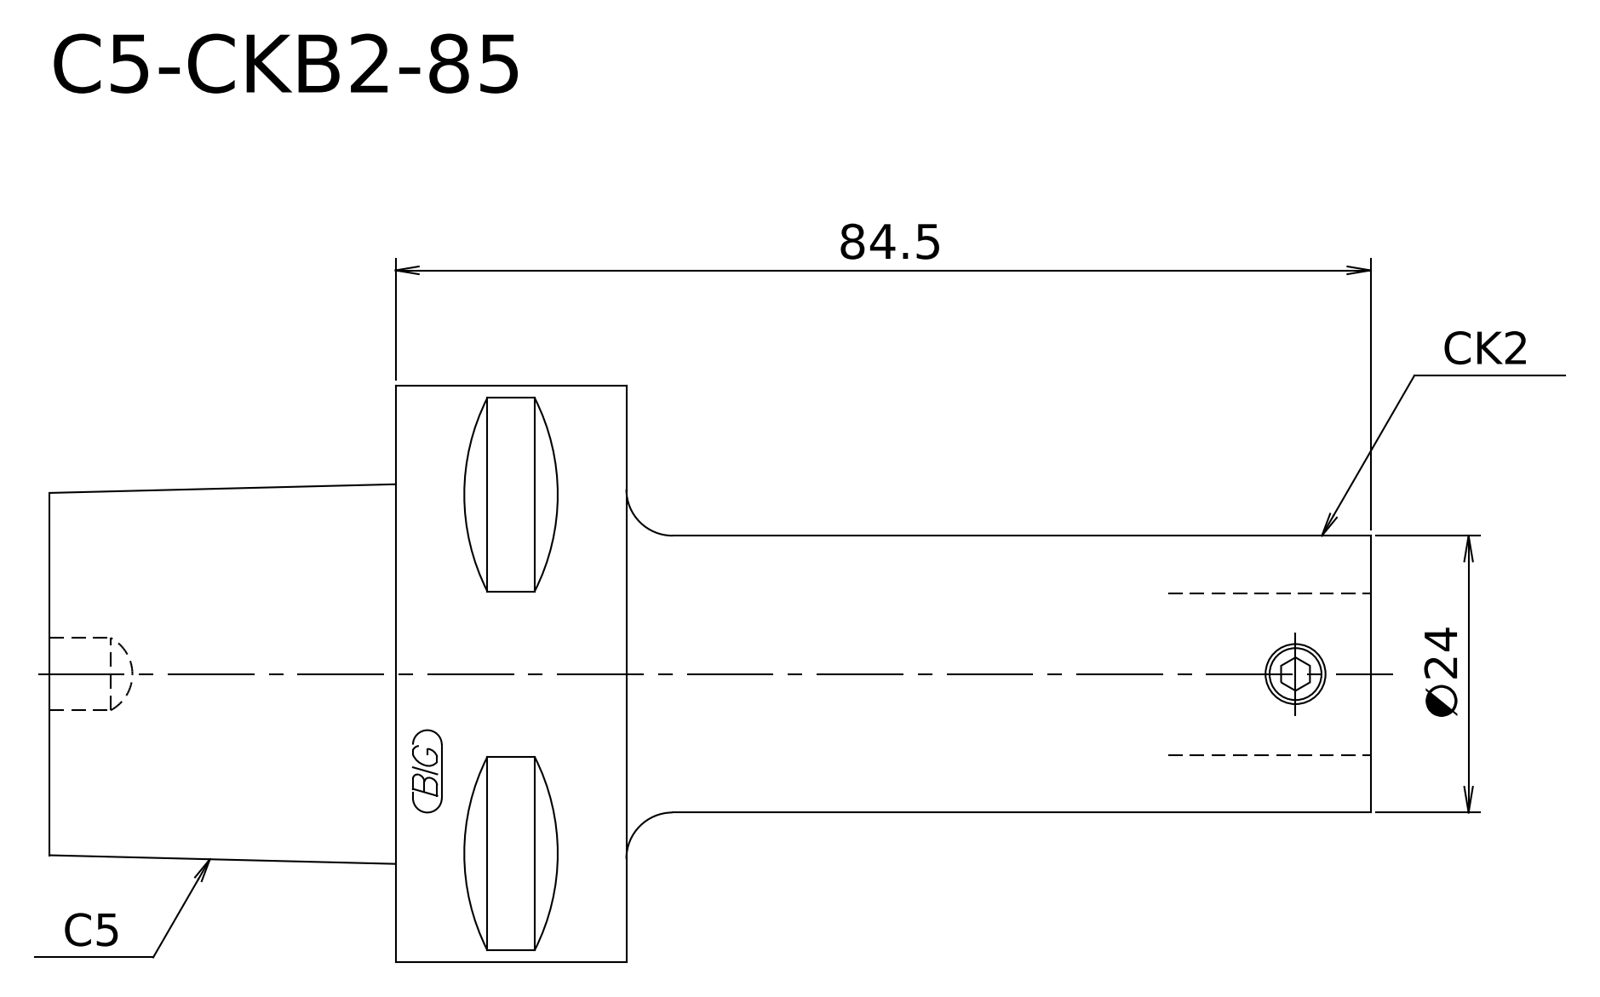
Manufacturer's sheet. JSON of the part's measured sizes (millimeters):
{"step_written_by": "Kubotek KeyCreator V8.5.1 (14335) (CONFIG_CONTROL_DESIGN)", "units": "millimeters", "bodies": {"solids": 1, "faces": 8, "planar": 4, "cylindrical": 2, "other": 2}, "overall_size": [114.5, 49.98, 49.98], "volume_mm3": 96308, "surface_area_mm2": 14933, "round_bosses_or_shafts": [[49.98, 1], [24, 1]], "face_to_face_distances": [20, 50, 30, 64.5, 84.5, 114.5]}
